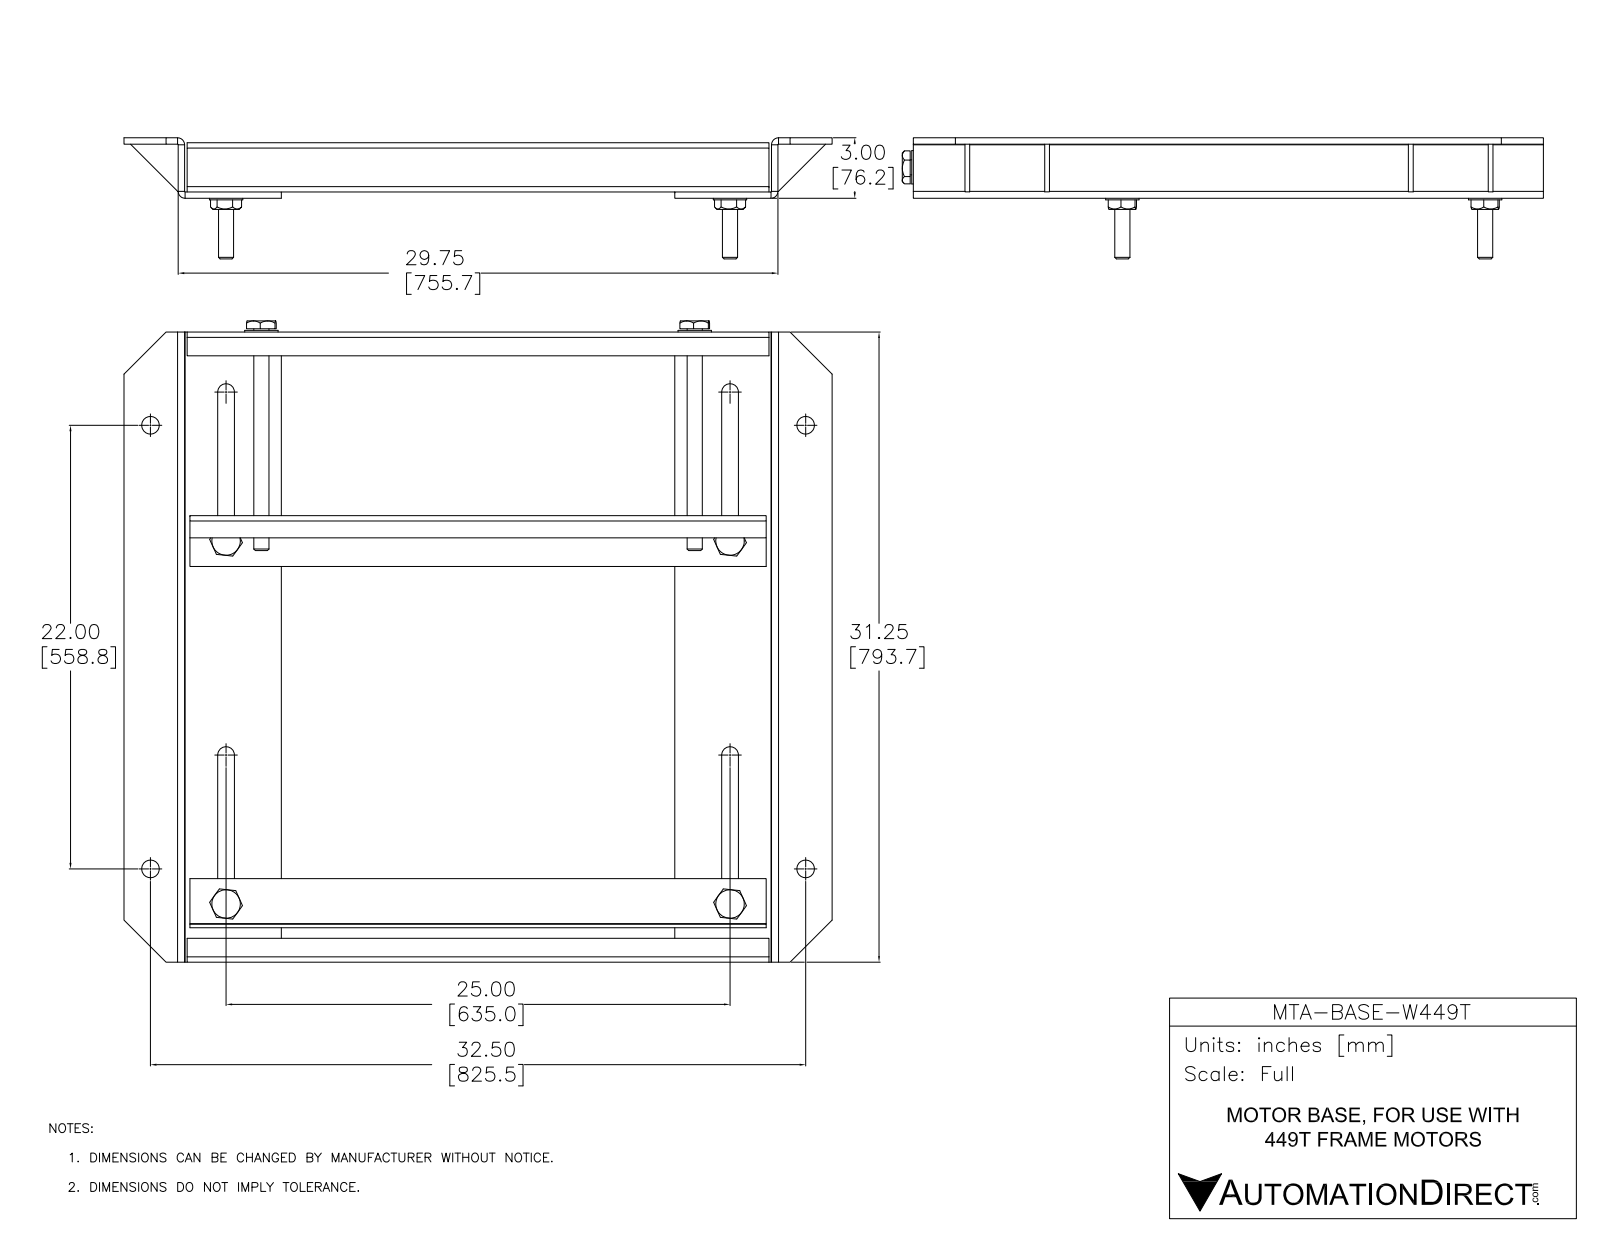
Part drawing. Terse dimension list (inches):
name: W449T nc
written by: SolidWorks 2017 (AUTOMOTIVE_DESIGN)
unit: in
bodies: 34 solids, 418 faces (240 planar, 110 cylindrical, 68 other)
size: 35.125 × 31.801 × 6.008
volume: 338.4 in³; area: 2 653 in²
holes: 6× ⌀0.75, 6× ⌀0.787, 4× ⌀0.752, 2× ⌀0.866, 2× ⌀0.875, 2× ⌀0.875
bosses: 6× ⌀1.654
rounds: 11× R0.029, 8× R0.413, 6× R0.265, 4× R0.344, 1× R0.206
face distances: 0.315, 0.236, 2.685, 2.205, 2.37, 3, 29.435, 0.177, 0.551, 2.134
hole spacings: 4.134, 6.857, 16.687, 18, 22, 24.035, 25, 28.803
